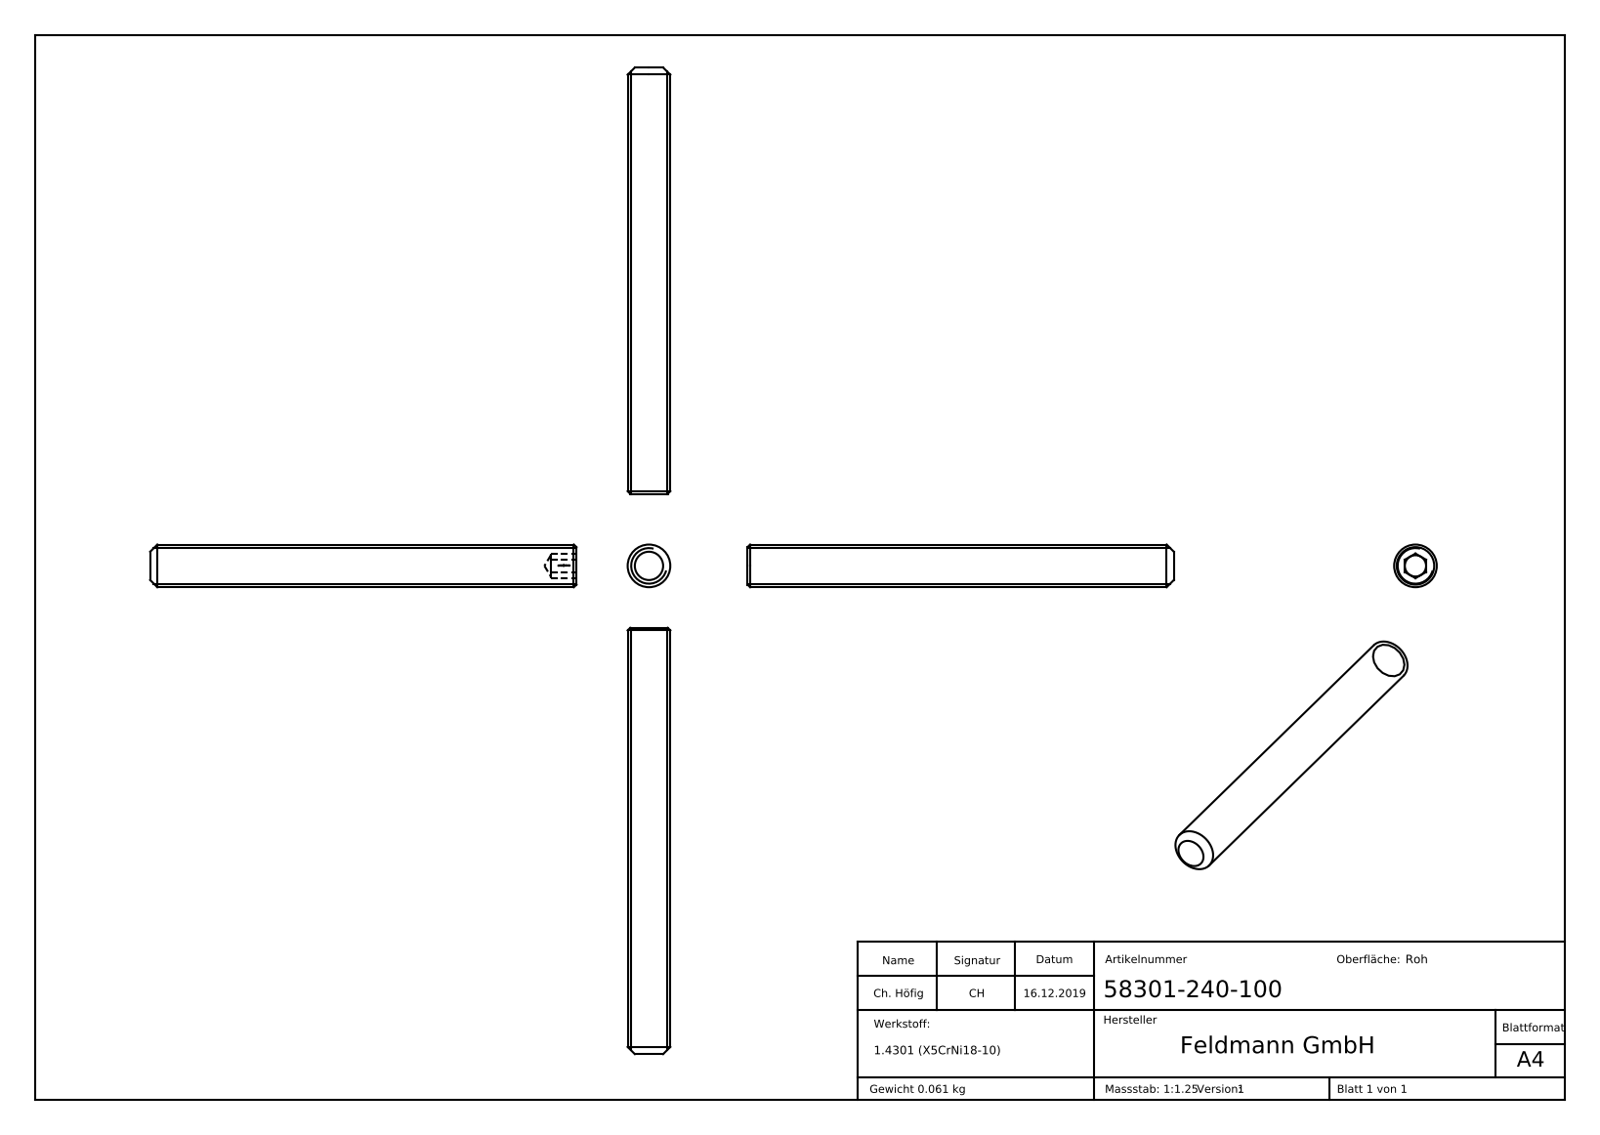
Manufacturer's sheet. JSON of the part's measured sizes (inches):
{"part_name": "58301-240-100", "step_written_by": "SolidWorks 2015 (CONFIG_CONTROL_DESIGN)", "units": "inches", "bodies": {"solids": 1, "faces": 295, "planar": 144, "cylindrical": 1, "other": 150}, "overall_size": [4.331, 0.394, 0.394], "volume_in3": 0.468, "surface_area_in2": 5.21, "round_bosses_or_shafts": [[0.394, 1]], "face_to_face_distances": [0.197, 3.937, 3.701, 0.236, 0.201, 0.015, 0.088, 0.074, 0.014, 0.02]}
